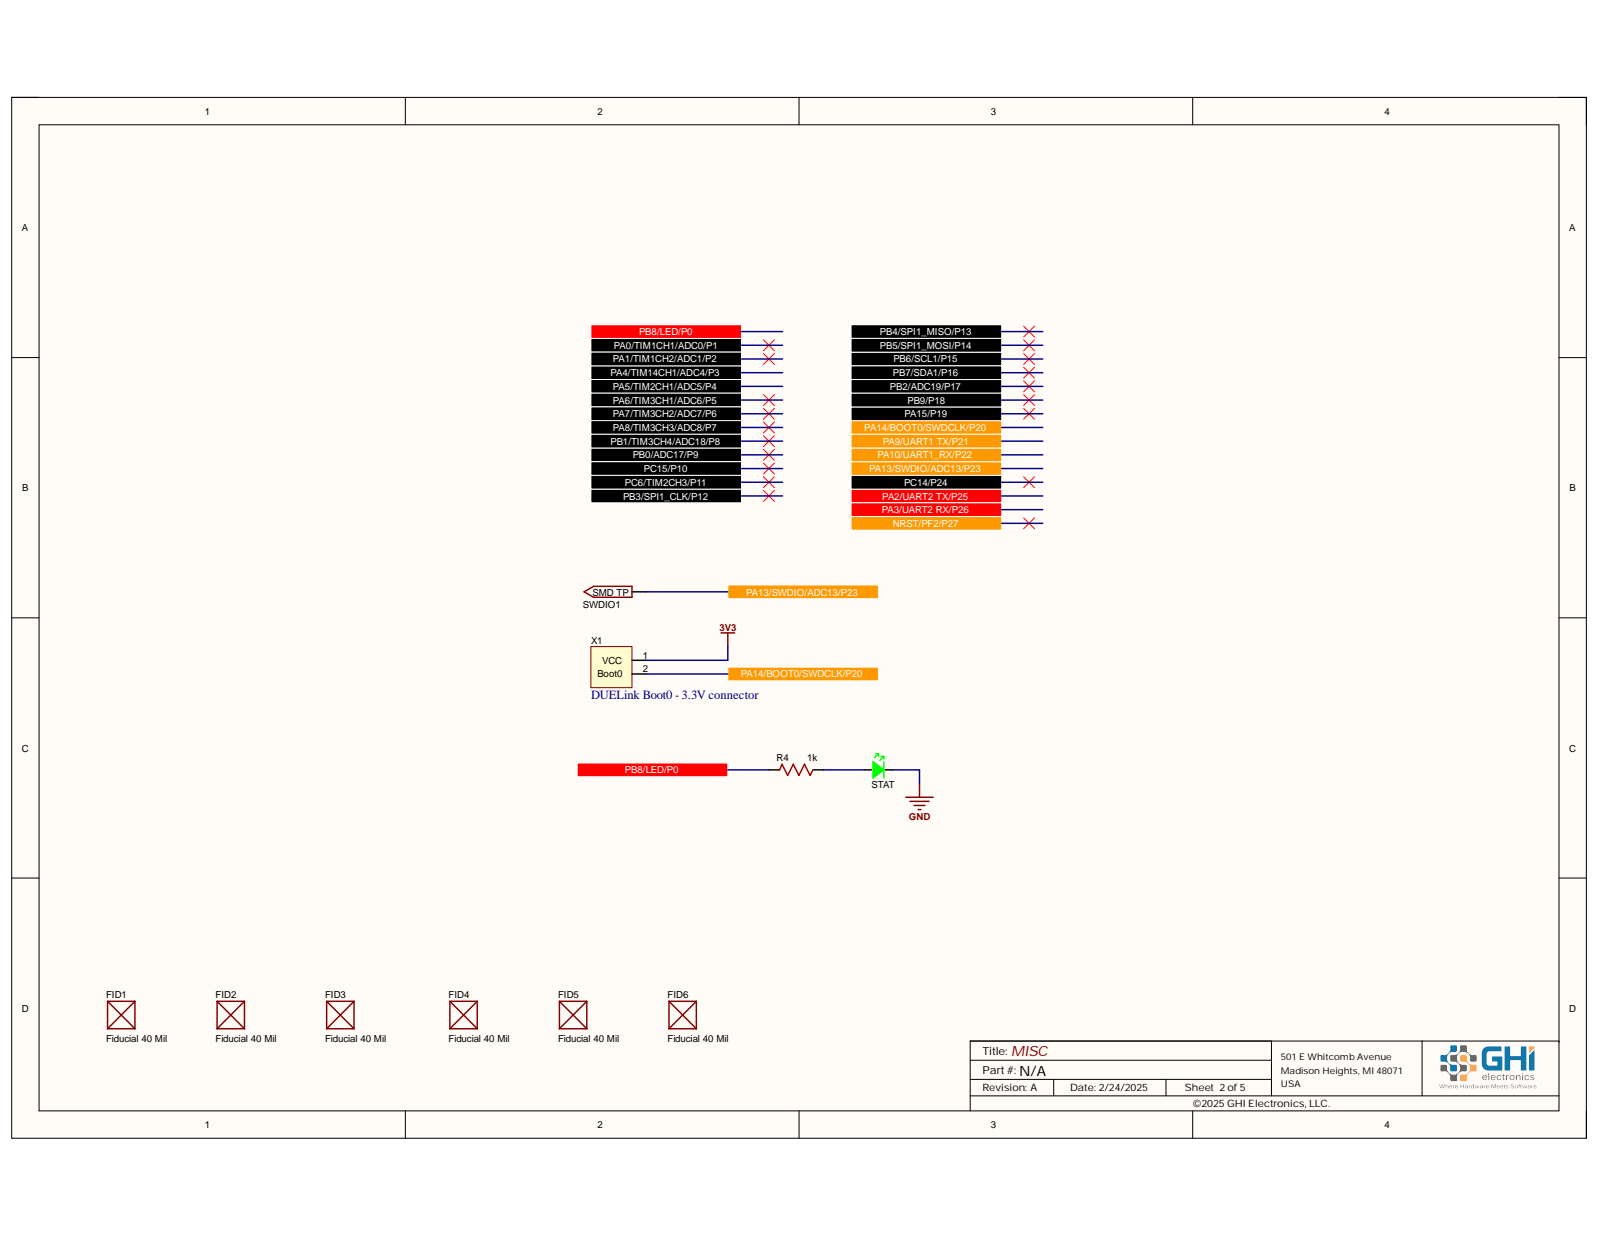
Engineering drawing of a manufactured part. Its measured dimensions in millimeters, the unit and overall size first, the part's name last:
Units: millimetres
Overall size (bounding box): 45 × 31.04 × 30
Round holes (diameter × count): ⌀1.6 ×10, ⌀1.02 ×4, ⌀1.82 ×4, ⌀2 ×4, ⌀0.6 ×3, ⌀1.02 ×2, ⌀3 ×2, ⌀12.32 ×2, ⌀13 ×2
Round bosses / shafts (diameter × count): ⌀13 ×4, ⌀2.53 ×4, ⌀16 ×2, ⌀9 ×2
Partial cylindrical surfaces — rounded edges, fillets, slot ends (radius × count): R0.12 ×35, R0.15 ×14, R0.16 ×4, R0.17 ×4, R0.24 ×4, R0.17 ×2, R0.18 ×2, R0.18 ×2
Main face-to-face distances: 1, 1.2, 8, 7, 6.8, 8.5, 9, 2.54, 5, 13
Hole centre spacings: 2.54, 35.04, 26, 26.48, 5, 5.08, 11.23, 11.69
Volume: 4 052 mm³ · Surface area: 9 118 mm²
Bodies: 250 solids, 4751 faces (4152 planar, 479 cylindrical, 120 other)
Part name (STEP PRODUCT): PCB; Board; J11; Conn_Harwin_M20-9990445_eec (+7 more)
STEP written by: Open CASCADE 7.5 (AUTOMOTIVE_DESIGN)
